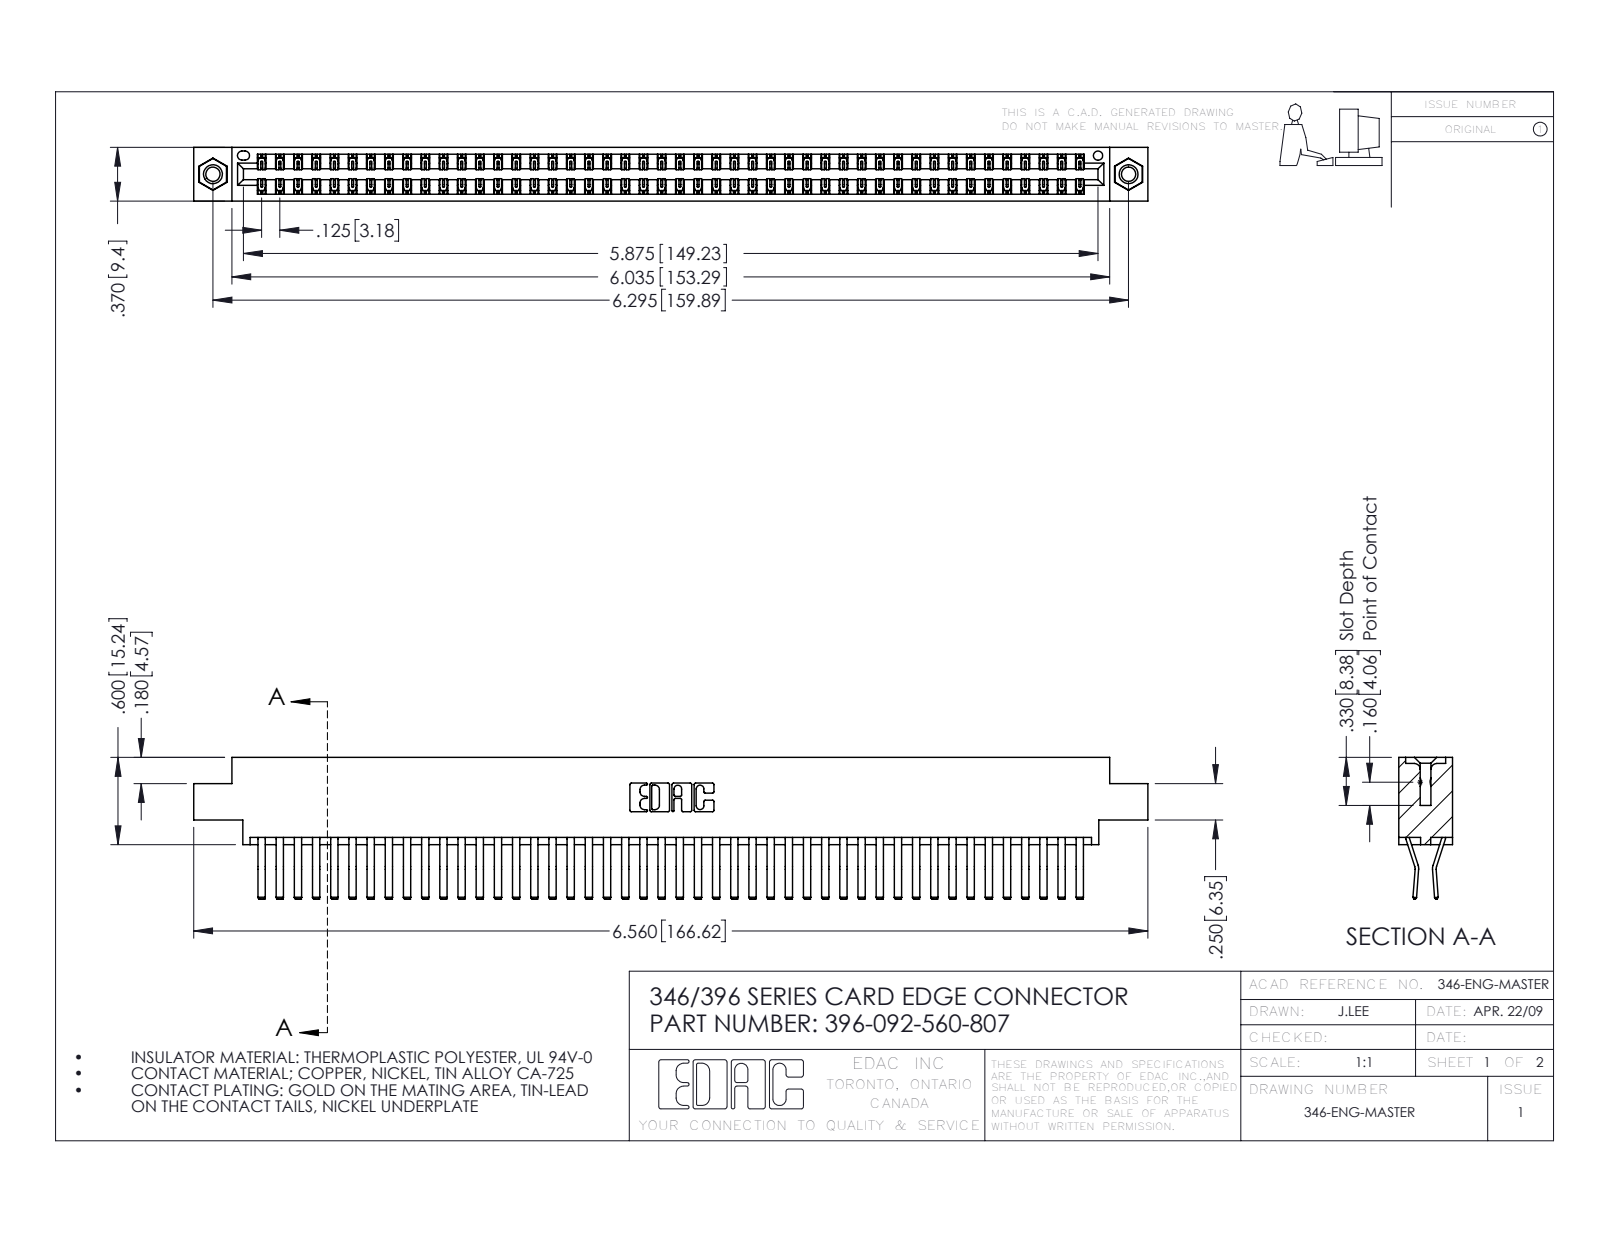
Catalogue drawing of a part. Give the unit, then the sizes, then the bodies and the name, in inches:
Units: inches
Overall size (bounding box): 6.56 × 0.975 × 0.37
Round holes (diameter × count): ⌀0.098 ×2, ⌀0.125 ×2, ⌀0.156 ×2, ⌀0.064 ×1
Round bosses / shafts (diameter × count): ⌀0.155 ×2
Partial cylindrical surfaces — rounded edges, fillets, slot ends (radius × count): R0.006 ×138, R0.01 ×22, R0.007 ×6, R0.031 ×6, R0.026 ×3, R0.01 ×2, R0.014 ×2, R0.022 ×2
Main face-to-face distances: 0.048, 0.322, 0.37, 0.025, 0.25, 0.072, 0.298, 0.275, 0.222, 0.148
Hole centre spacings: 0.246, 6.086, 6.295
Volume: 1.02 in³ · Surface area: 38.53 in²
Bodies: 95 solids, 5154 faces (3332 planar, 1806 cylindrical, 16 other)
Part name (STEP PRODUCT): 396-092-560-807; 345-292-001_560 Tail; 345-250-001_345-250-005-103; 346 Part_0.170 Offset - 0.156 Dia-TI
STEP written by: SolidWorks 2016 (CONFIG_CONTROL_DESIGN)
